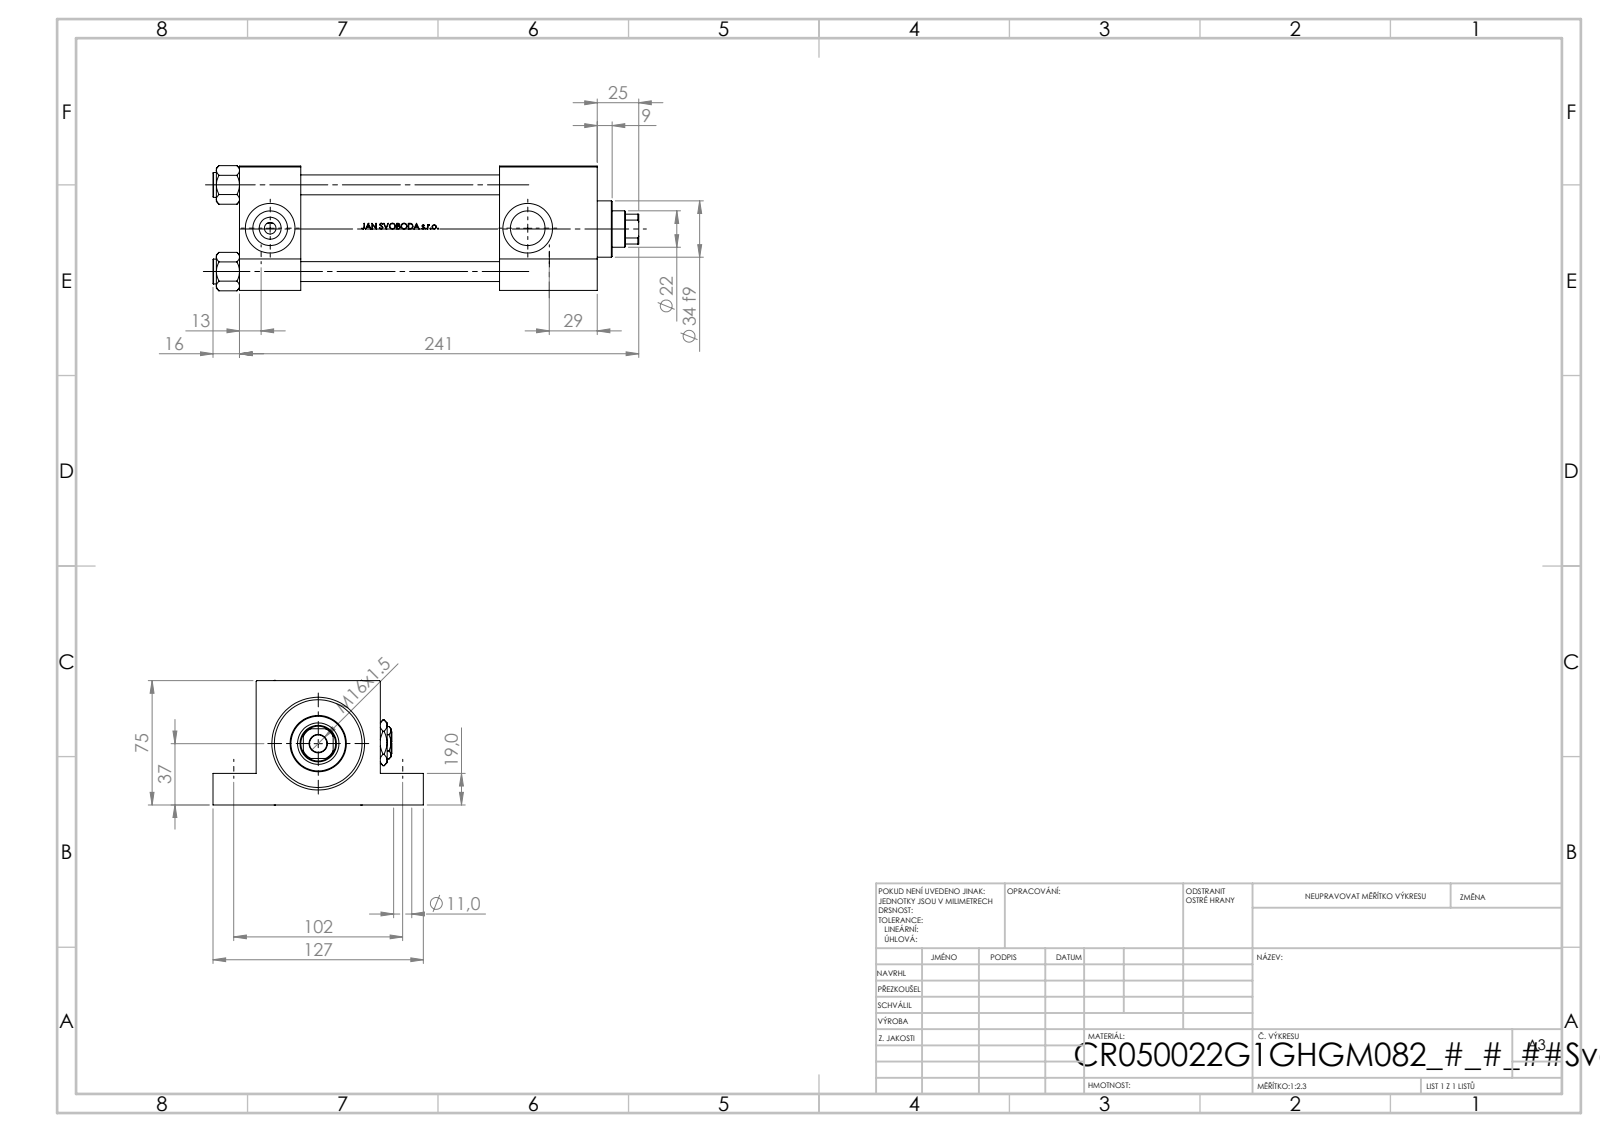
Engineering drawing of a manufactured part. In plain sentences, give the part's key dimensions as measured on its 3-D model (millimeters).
The part is named "V215CR_G_Body; V215CR_VCP_G; NUT_M5_G; V215CR_G_TYCINKA (+2 more)". Its 3-D file was written by "SolidWorks 2019 (CONFIG_CONTROL_DESIGN)". It is 12 solids with 1134 faces: 454 planar, 128 cylindrical and 552 other. Overall it measures 257 by 127 by 75.54 millimeters. Its volume is 834 989 cubic millimeters and its surface area 195 585 square millimeters. Round holes: 4 of diameter 11, 4 of diameter 12, 2 of diameter 7, 2 of diameter 20.96, 2 of diameter 30, 1 of diameter 10.5, 1 of diameter 22, 1 of diameter 25, 1 of diameter 41, 1 of diameter 50, 1 of diameter 53. Round bosses or shafts: 4 of diameter 15, 1 of diameter 56, 1 of diameter 34. Partial cylindrical surfaces (rounded edges, fillets, slot ends): 1 of radius 10.5. The main face-to-face distances are 75, 37, 216, 179, 19, 56, 157, 120, 59, 26. The hole center spacings are 52.3, 36.63, 37.34, 73.96, 102, 174, 201.69, 155.5.
